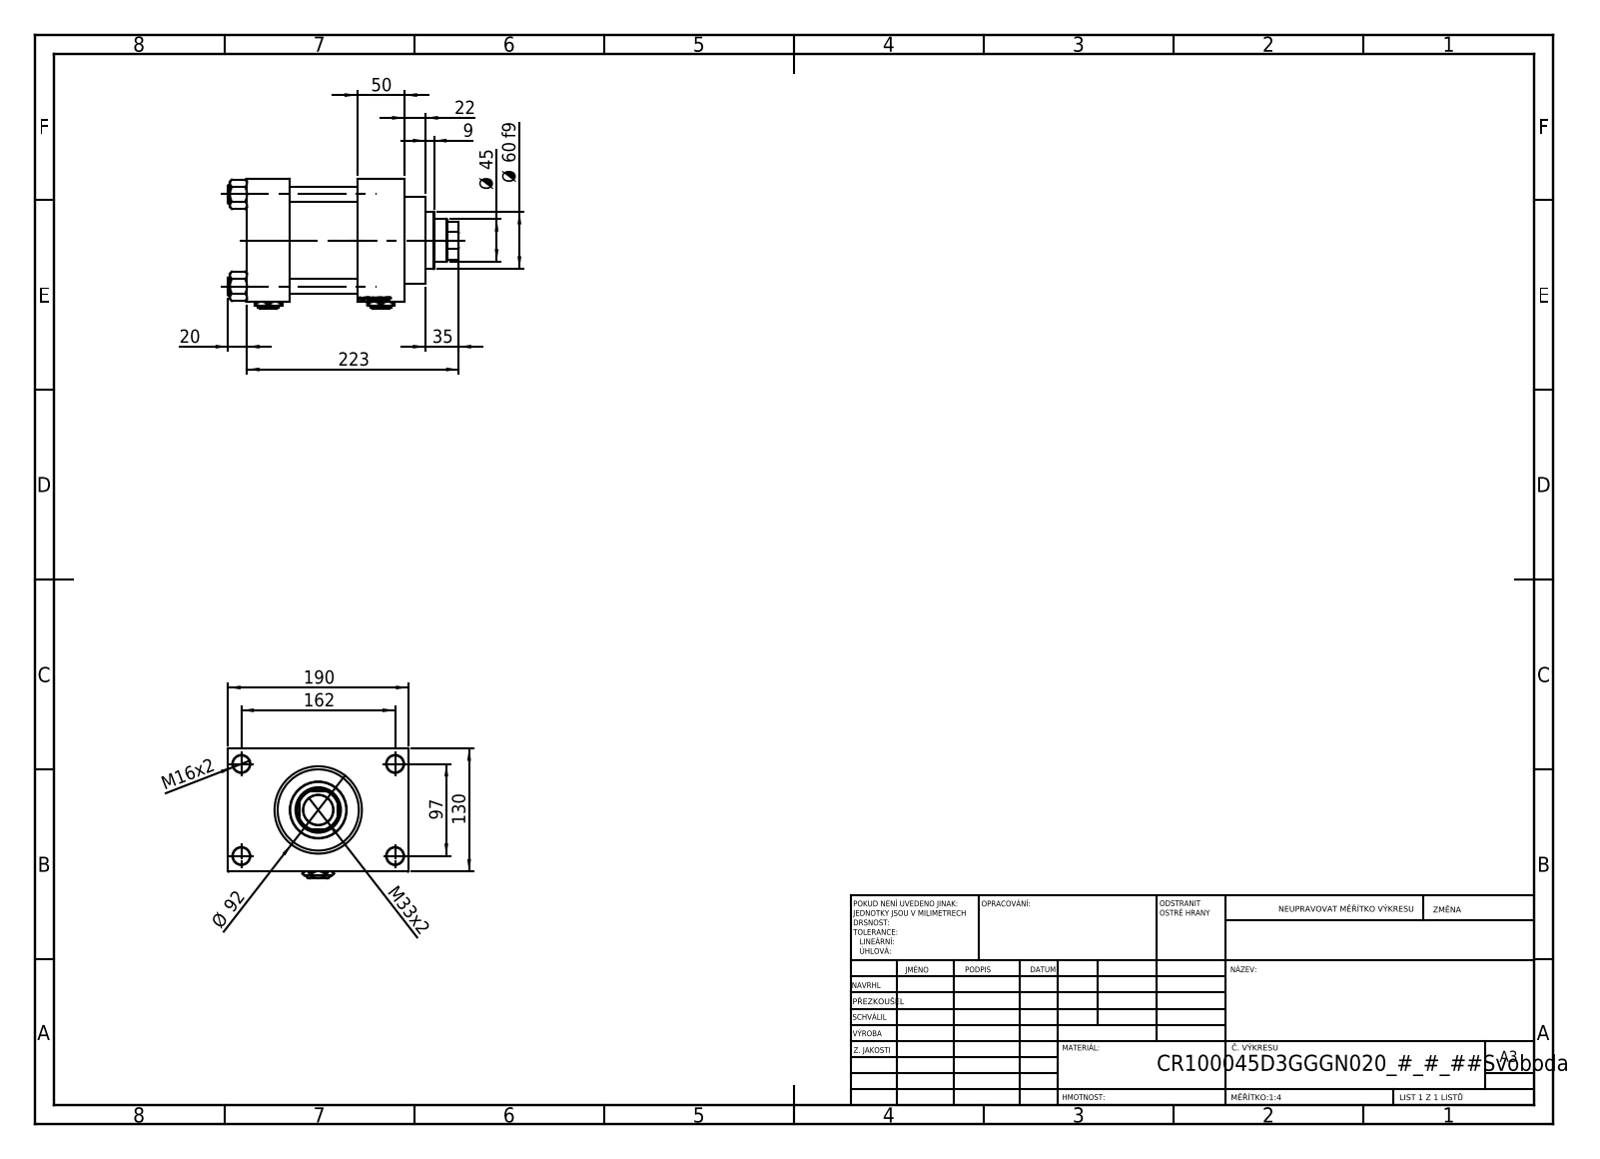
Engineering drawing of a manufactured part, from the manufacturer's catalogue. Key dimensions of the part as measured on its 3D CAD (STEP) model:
Part name (STEP PRODUCT): V215_VC_A; Zatka_pro_OIL_PORT; V215CR_VCP_D; V215CR_D_Body (+2 more)
STEP written by: SolidWorks 2019 (CONFIG_CONTROL_DESIGN)
Units: millimetres
Bodies: 13 solids, 1253 faces (593 planar, 100 cylindrical, 560 other)
Overall size (bounding box): 243 × 190 × 137
Volume: 2 592 000 mm³ · Surface area: 359 312 mm²
Round holes (diameter × count): ⌀16 ×4, ⌀18 ×4, ⌀7 ×2, ⌀26.44 ×2, ⌀35 ×2, ⌀31.5 ×1, ⌀45 ×1, ⌀48 ×1, ⌀76 ×1, ⌀85.5 ×1, ⌀100 ×1
Round bosses / shafts (diameter × count): ⌀19 ×4, ⌀106 ×1, ⌀92 ×1, ⌀60 ×1
Partial cylindrical surfaces — rounded edges, fillets, slot ends (radius × count): R22 ×1
Main face-to-face distances: 130, 45, 116, 71, 166, 121, 50, 160, 30, 20
Hole centre spacings: 32.55, 68.52, 94.41, 96.9, 102.27, 129.45, 161.73, 97
